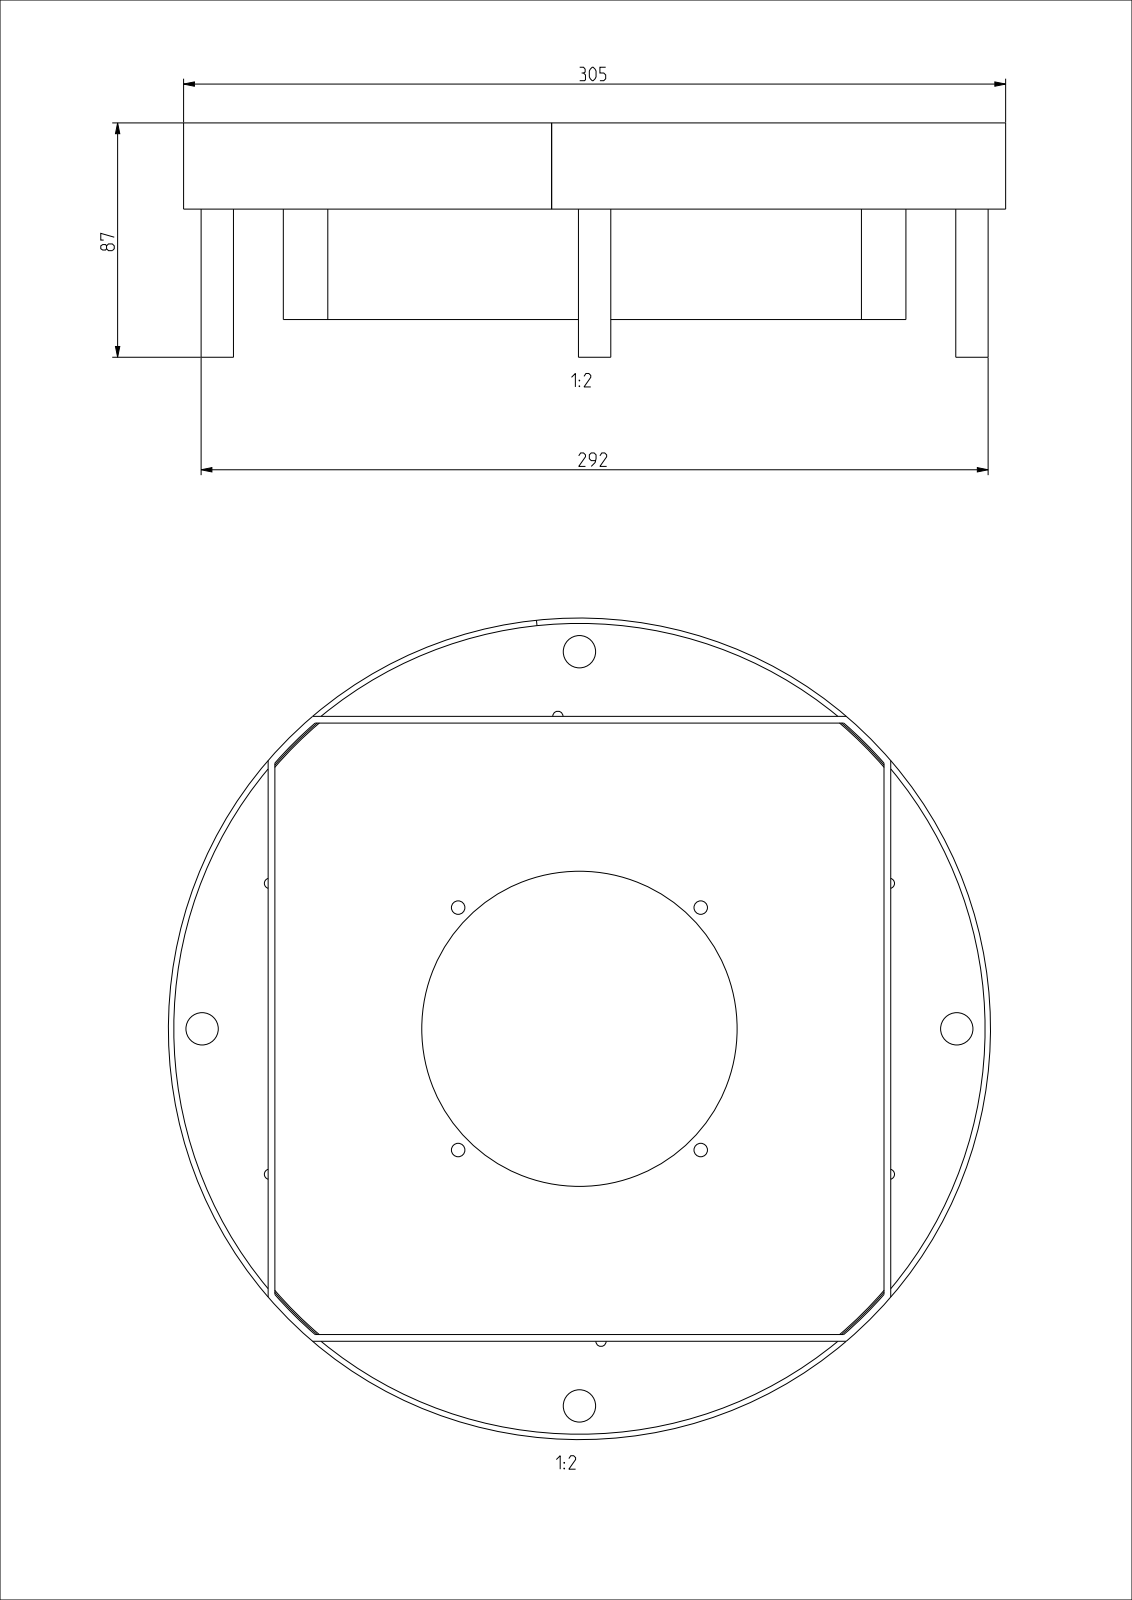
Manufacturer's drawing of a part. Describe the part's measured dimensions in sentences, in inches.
The part is named "T-00702; T-00703; T-00704; T-00709 (+8 more)". Its 3-D file was written by "CREO PARAMETRIC BY PTC INC, 2022024 (AUTOMOTIVE_DESIGN)". It is 9 solids with 146 faces: 74 planar, 72 cylindrical and 0 other. Overall it measures 12.008 by 12.008 by 3.425 inches. Its volume is 57.87 cubic inches and its surface area 834.4 square inches. Round holes: 6 of diameter 0.15, 4 of diameter 0.197, 4 of diameter 0.398, 1 of diameter 4.606. Round bosses or shafts: 4 of diameter 0.472, 4 of diameter 0.388, 1 of diameter 12.008, 1 of diameter 11.85, 1 of diameter 11.772, 1 of diameter 11.732, 1 of diameter 11.614. Partial cylindrical surfaces (rounded edges, fillets, slot ends): 8 of radius 0.02, 1 of radius 5.906. The main face-to-face distances are 0.079, 0.472, 0.394, 0.098, 0.591, 0.669, 0.197, 8.996, 0.118, 0.512. The hole center spacings are 4.139, 7.496, 2.343, 2.506, 2.779, 3.543, 4.774, 5.002.
